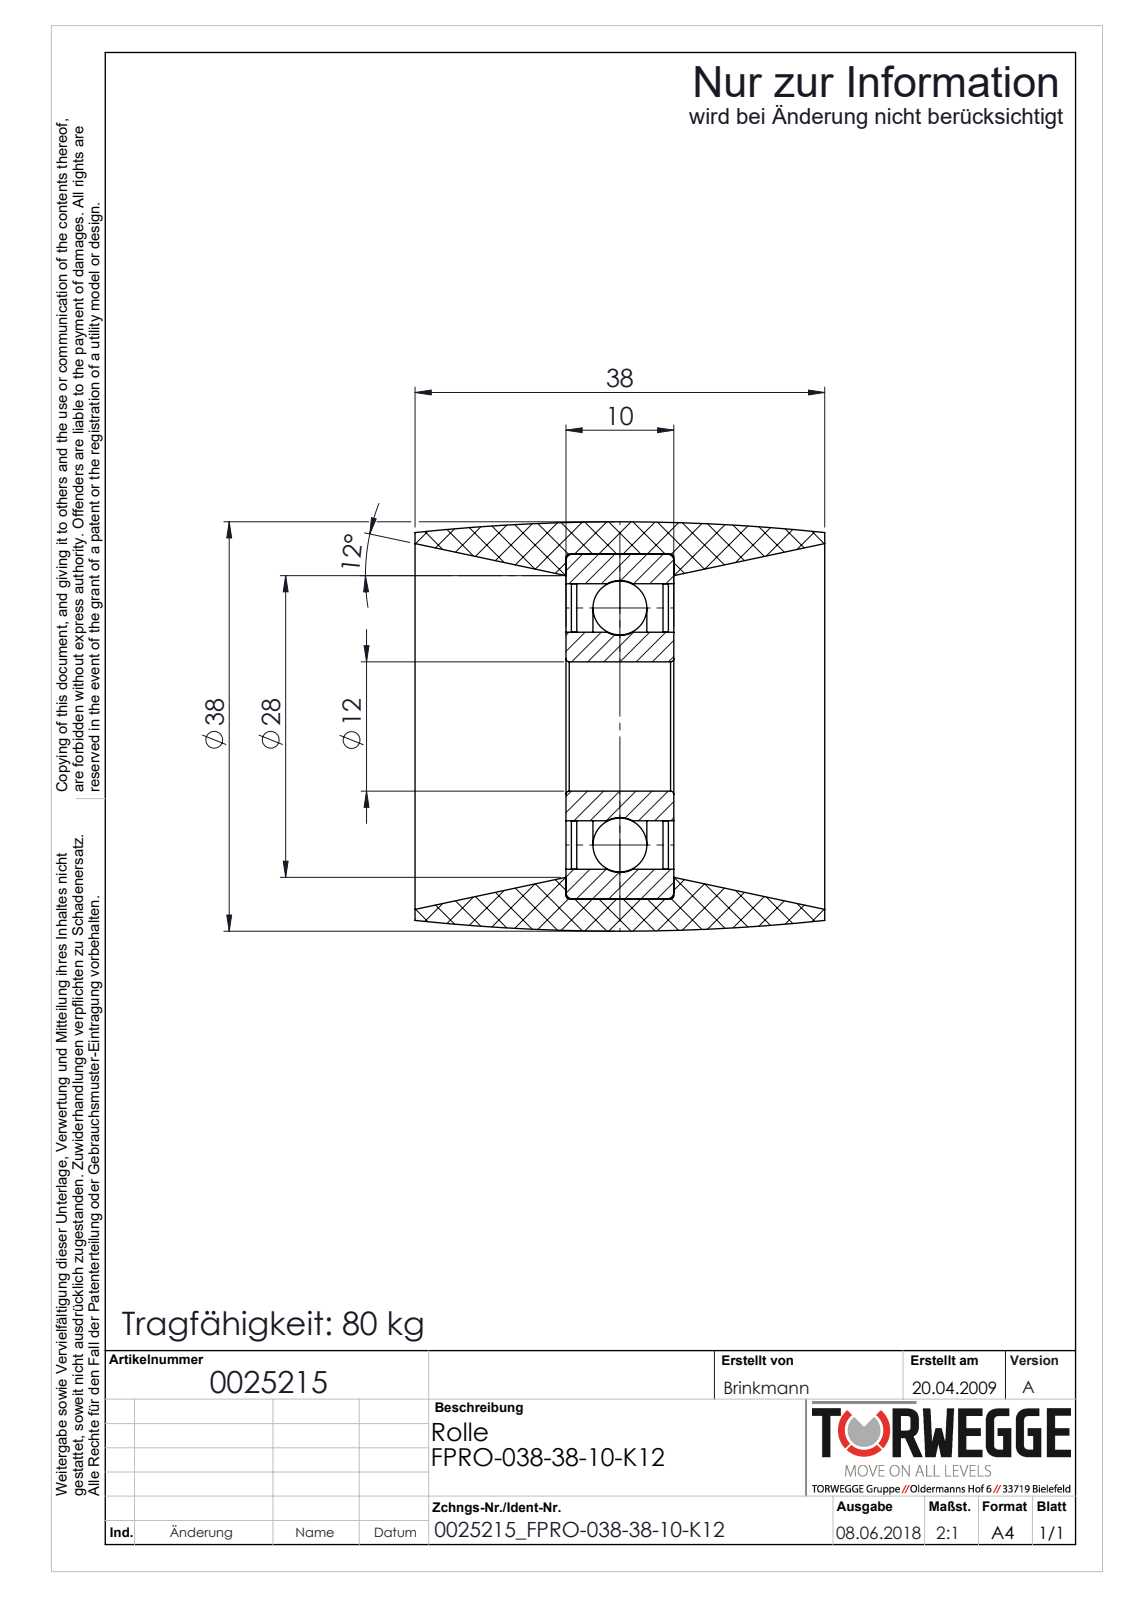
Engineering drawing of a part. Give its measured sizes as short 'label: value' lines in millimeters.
name: 0025215_FPRO-038-38-10-K12
written by: SolidWorks 2018 (AUTOMOTIVE_DESIGN)
unit: mm
bodies: 6 solids, 62 faces (12 planar, 22 cylindrical, 28 other)
size: 38 × 38 × 38
volume: 17 814 mm³; area: 14 777 mm²
holes: 1× ⌀12, 1× ⌀17.5, 1× ⌀26.5, 1× ⌀32
face distances: 0.5, 9, 1, 9.5, 8.5, 10, 8, 14, 14.5, 15
